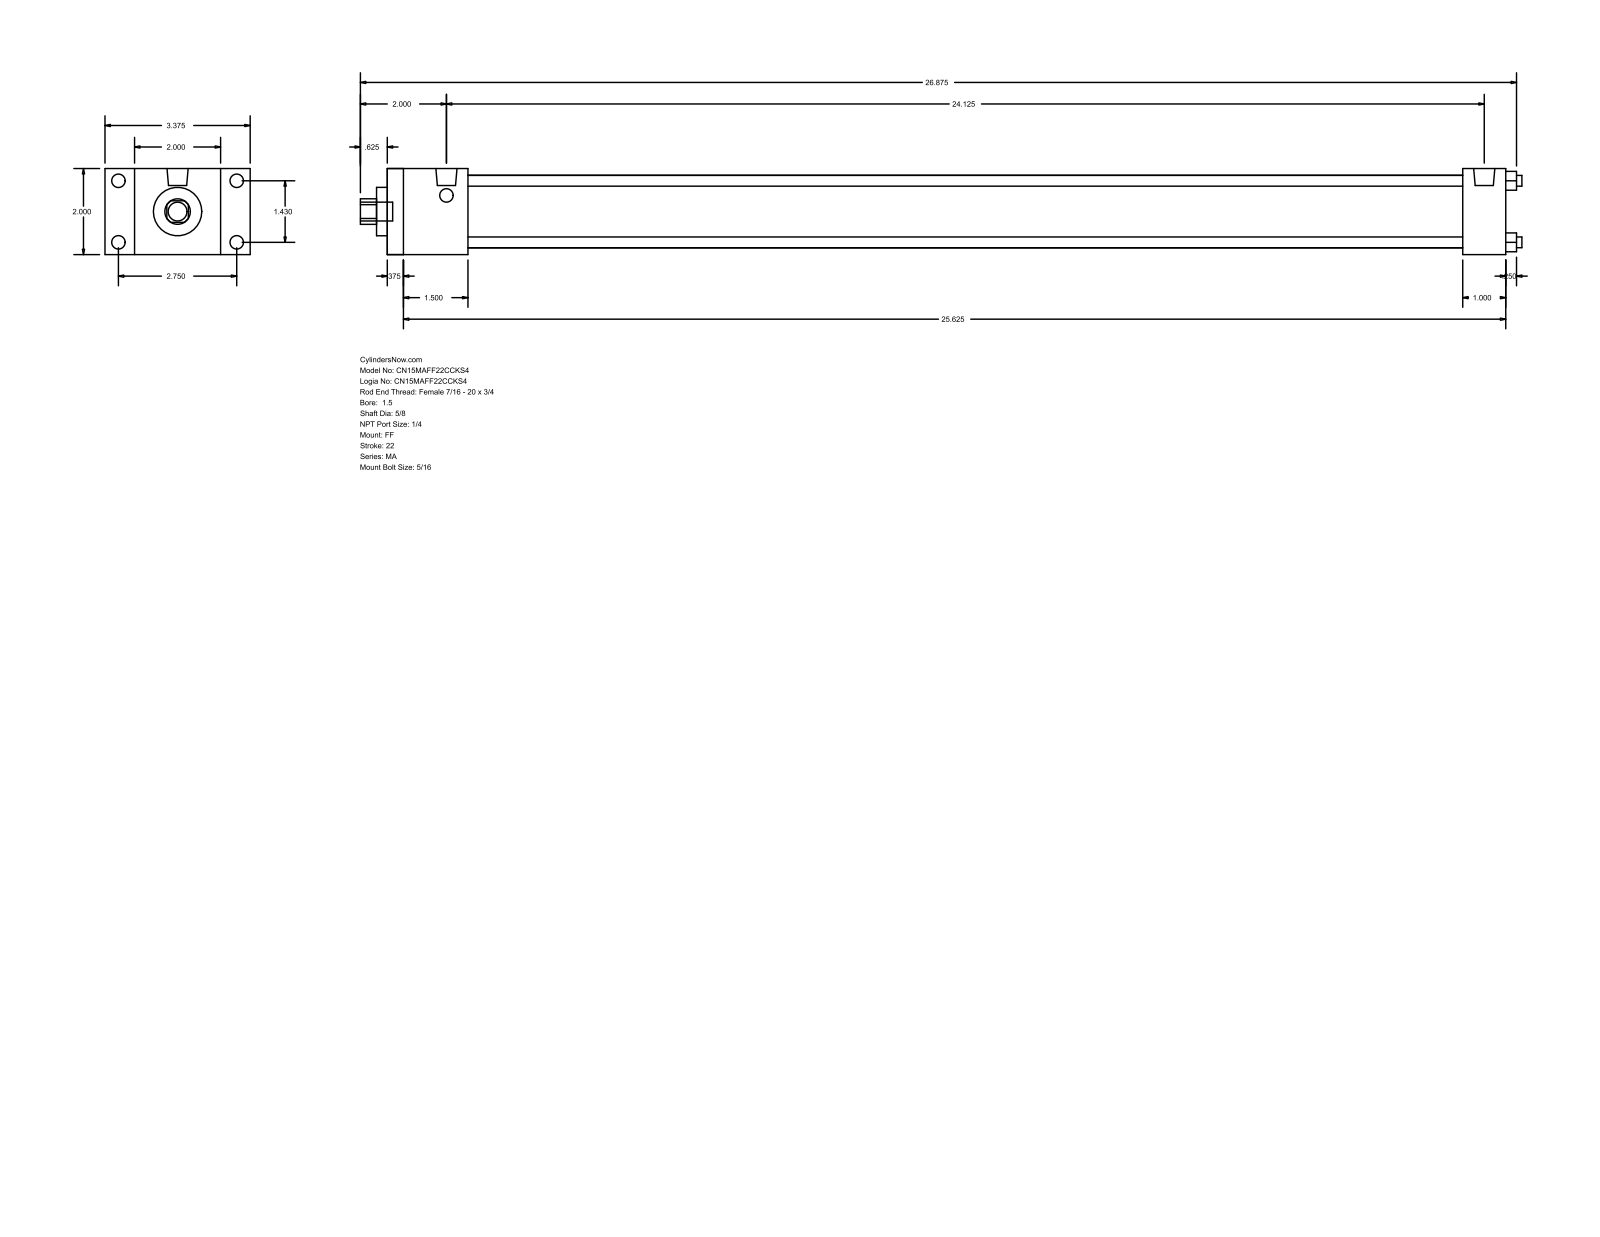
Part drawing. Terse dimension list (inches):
name: MA_FF__0150_0.625
written by: GSSL Pune (CONFIG_CONTROL_DESIGN)
unit: in
bodies: 0 solids, 92 faces (64 planar, 28 cylindrical, 0 other)
size: 27 × 3.375 × 2
holes: 4× ⌀0.25, 1× ⌀0.625, 1× ⌀1.125, 1× ⌀1.69
bosses: 8× ⌀0.313, 2× ⌀0.492, 1× ⌀0.437
rounds: 1× R0.297
face distances: 2, 26, 0.375, 25.625, 1.875, 25, 1.5, 24.625, 23.125, 24.125
hole spacings: 1.011, 1.43, 2.022
